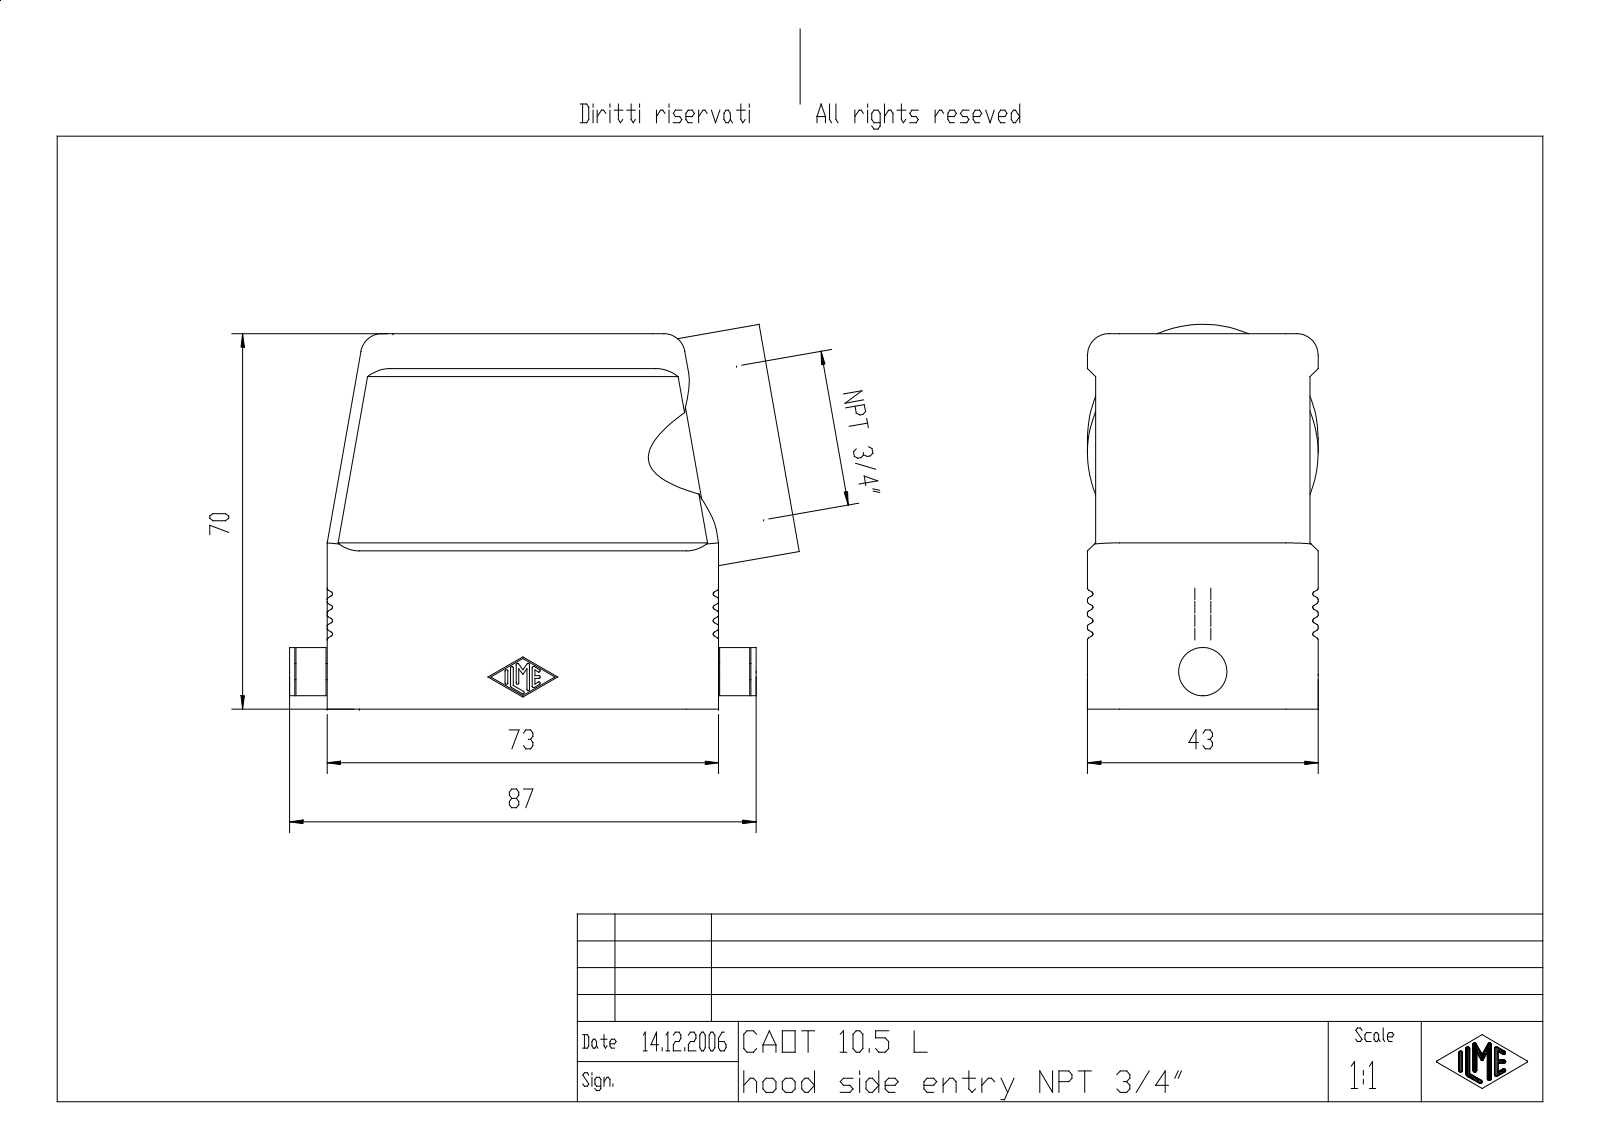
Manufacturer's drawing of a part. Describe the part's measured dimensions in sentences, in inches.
The part is named "MSBO11097". Its 3-D file was written by "Creo Elements/Direct Modeling 18.0B 02-Dec-2011 (C) Parametric Technology GmbH (AUTOMOTIVE_DESIGN)". It is 1 solid with 523 faces: 198 planar, 213 cylindrical and 112 other. Overall it measures 3.741 by 2.824 by 1.693 inches. Its volume is 4.295 cubic inches and its surface area 62.73 square inches. Round holes: 4 of diameter 0.097, 4 of diameter 0.122. Round bosses or shafts: 1 of diameter 1.693, 1 of diameter 0.354, 1 of diameter 0.118. Partial cylindrical surfaces (rounded edges, fillets, slot ends): 64 of radius 0.016, 14 of radius 0.01, 10 of radius 0.118, 10 of radius 0.236, 4 of radius 0.079, 4 of radius 0.157, 4 of radius 0.197. The main face-to-face distances are 0.059, 0.118, 1.575, 1.516, 1.457, 1.634, 0.335, 0.453, 2.756, 2.303. The hole center spacings are 1.063, 2.244, 2.483.
